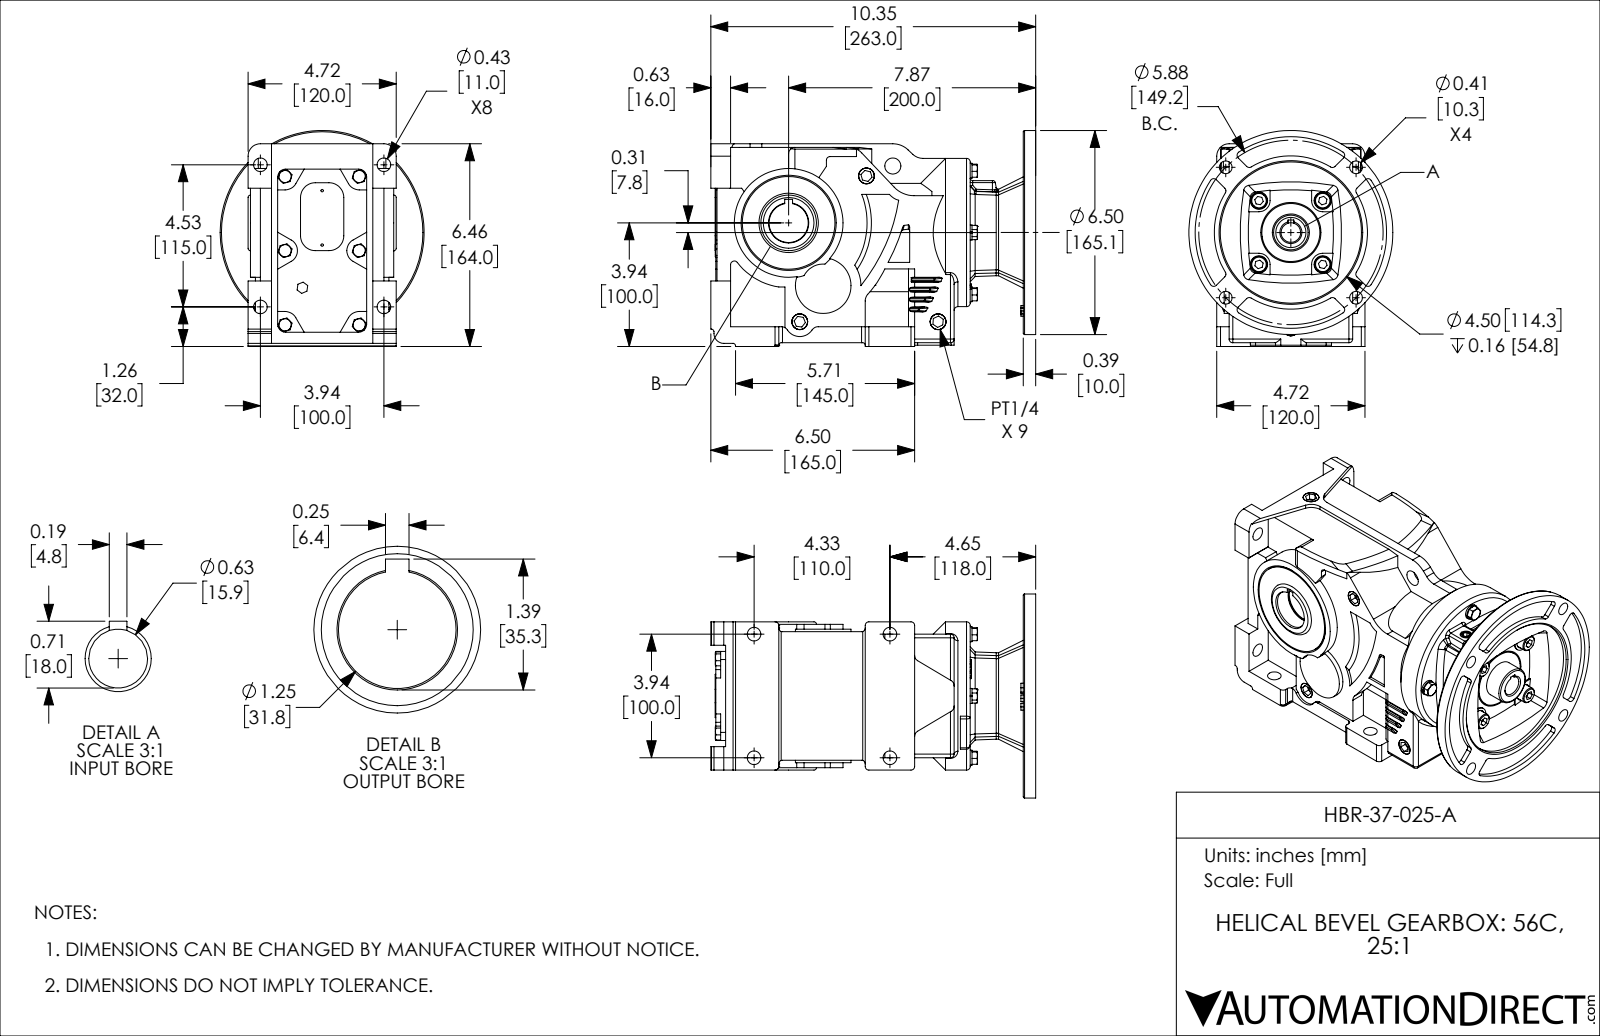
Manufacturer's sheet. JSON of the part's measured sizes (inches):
{"part_name": "HBR-37-025-A", "step_written_by": "SolidWorks 2018 (AUTOMOTIVE_DESIGN)", "units": "inches", "bodies": {"solids": 1, "faces": 1082, "planar": 491, "cylindrical": 289, "other": 302}, "overall_size": [10.354, 6.88, 6.5], "volume_in3": 200.9, "surface_area_in2": 390.7, "round_holes": [[0.433, 8], [0.24, 4], [0.276, 4], [0.406, 4], [0.551, 4], [0.079, 2], [0.512, 1], [0.625, 1], [0.846, 1], [1.25, 1], [1.327, 1], [4.5, 1]], "round_bosses_or_shafts": [[0.512, 4], [0.48, 4], [0.236, 4], [6.5, 1], [4.724, 1], [3.465, 1], [2.953, 1], [1.85, 1]], "partial_cylinders_radius": [[0.118, 42], [0.039, 18], [0.197, 11], [0.079, 10], [0.394, 10], [0.472, 6], [0.256, 4], [0.354, 4]], "face_to_face_distances": [0.157, 0.394, 0.472, 0.315, 0.236, 0.118, 0.079, 4.252, 0.63, 3.78], "hole_center_spacings": [1.393, 2.08, 3.153, 3.27, 4.548, 3.937, 1.437, 1.5]}
